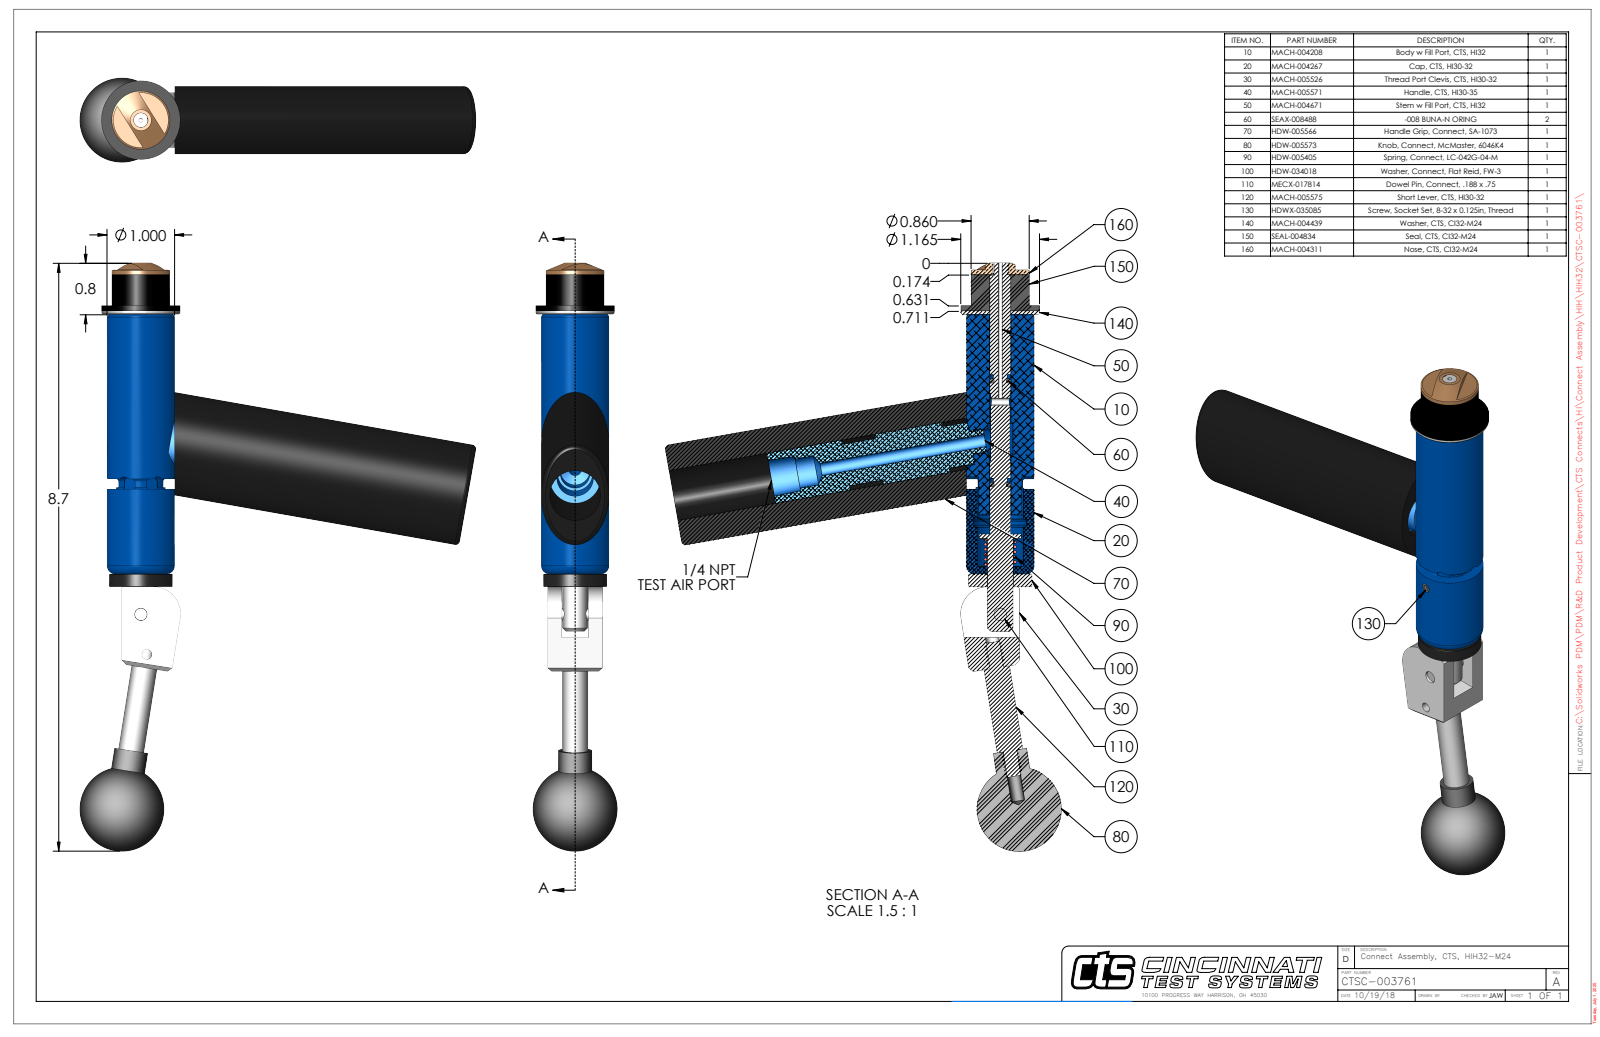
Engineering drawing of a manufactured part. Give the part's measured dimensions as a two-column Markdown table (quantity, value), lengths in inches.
| quantity | value |
| --- | --- |
| part name | CTSC-003761 |
| STEP written by | SolidWorks 2023 (AUTOMOTIVE_DESIGN) |
| units | inches |
| bodies | 10 solids, 312 faces (116 planar, 127 cylindrical, 69 other) |
| overall size | 8.692 × 5.856 × 1.25 |
| volume | 9.603 in³ |
| surface area | 80.24 in² |
| round holes (diameter × count) | 0.201 × 2, 0.063 × 1, 0.109 × 1, 0.136 × 1, 0.15 × 1, 0.187 × 1, 0.189 × 1, 0.213 × 1, 0.31 × 1, 0.314 × 1, 0.316 × 1, 0.385 × 1 |
| round bosses / shafts (diameter × count) | 0.25 × 2, 0.201 × 2, 1.165 × 1, 1 × 1, 0.936 × 1, 0.86 × 1, 0.75 × 1, 0.62 × 1 |
| partial cylindrical surfaces (radius × count) | 0.093 × 6, 0.029 × 2, 0.061 × 1, 0.325 × 1, 0.375 × 1, 0.4 × 1, 0.454 × 1 |
| main face-to-face distances | 0.05, 0.21, 0.602, 0.537, 0.587, 4.42, 3.883, 3.833, 0.812, 4.608 |
| hole center spacings | 0.599, 1.658, 2.252 |
